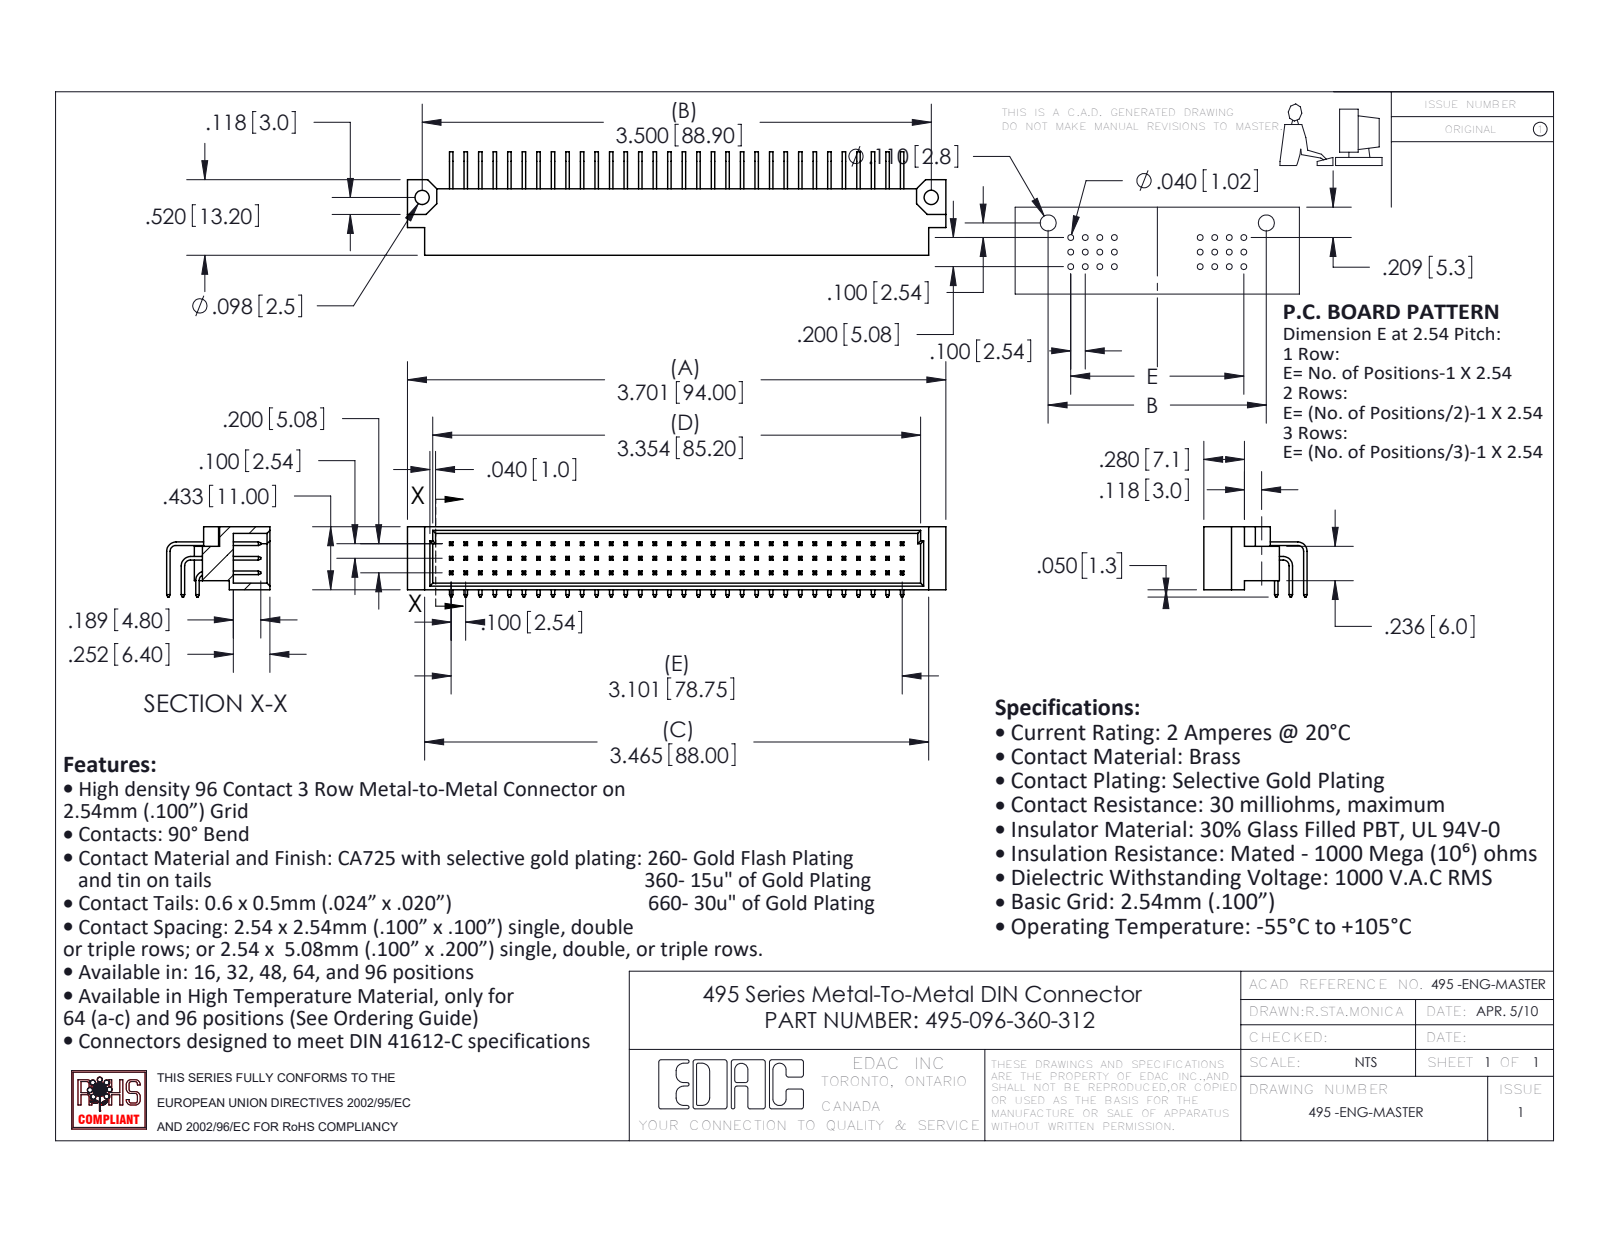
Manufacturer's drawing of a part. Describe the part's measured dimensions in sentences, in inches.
The part is named "495-290-3; 495-096-360-312; 495-290-2; 495 Part_96 (+1 more)". Its 3-D file was written by "SolidWorks 2020 (AUTOMOTIVE_DESIGN)". It is 97 solids with 2161 faces: 1965 planar, 196 cylindrical and 0 other. Overall it measures 3.701 by 0.711 by 0.483 inches. Its volume is 0.404 cubic inches and its surface area 17.74 square inches. Round holes: 2 of diameter 0.098. Partial cylindrical surfaces (rounded edges, fillets, slot ends): 3 of radius 0.04, 3 of radius 0.065. The main face-to-face distances are 0.1, 0.024, 0.2, 0.205, 0.045, 0.388, 0.124, 0.076, 0.433, 0.343. The hole center spacings are 3.5.
